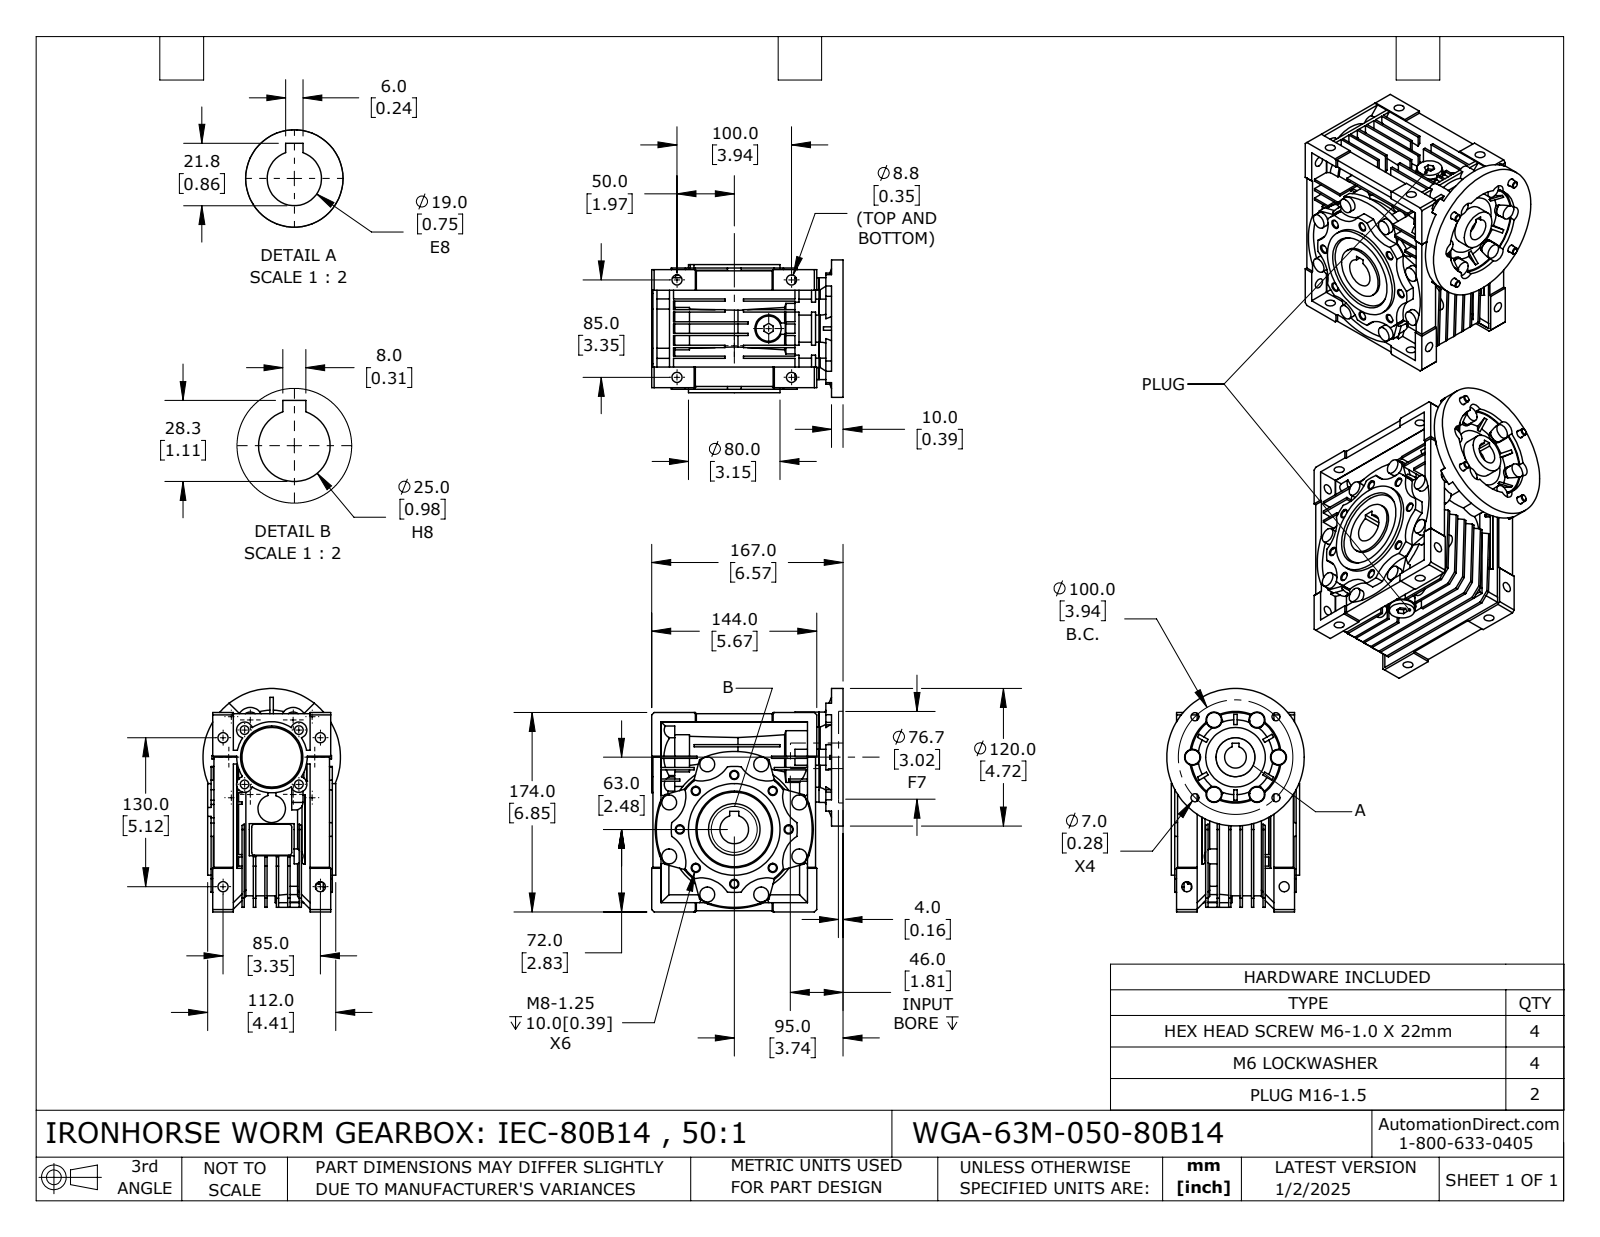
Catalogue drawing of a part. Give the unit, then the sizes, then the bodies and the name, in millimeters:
Units: millimetres
Overall size (bounding box): 195 × 172.5 × 120
Round holes (diameter × count): ⌀6.65 ×8, ⌀8.78 ×8, ⌀6.1 ×4, ⌀7 ×4, ⌀7.56 ×4, ⌀14.5 ×2, ⌀19 ×1, ⌀20 ×1, ⌀25 ×1, ⌀34 ×1, ⌀37 ×1, ⌀45 ×1
Round bosses / shafts (diameter × count): ⌀13 ×14, ⌀14 ×6, ⌀12.2 ×4, ⌀6 ×4, ⌀24 ×3, ⌀22 ×2, ⌀15.8 ×2, ⌀13.7 ×2
Partial cylindrical surfaces — rounded edges, fillets, slot ends (radius × count): R7 ×10, R27 ×8, R6.98 ×6, R11 ×6, R2.5 ×4, R8.35 ×1, R29.5 ×1, R30.5 ×1
Main face-to-face distances: 10, 8, 20, 2, 30, 18, 12, 7, 40, 1
Hole centre spacings: 36.36, 47.5, 60.19, 67.18, 87.77, 16.5, 33.5, 47.38
Volume: 1 847 000 mm³ · Surface area: 350 234 mm²
Bodies: 16 solids, 1442 faces (853 planar, 413 cylindrical, 176 other)
Part name (STEP PRODUCT): WGA-63M-050-80B14
STEP written by: SolidWorks 2024 (CONFIG_CONTROL_DESIGN)
